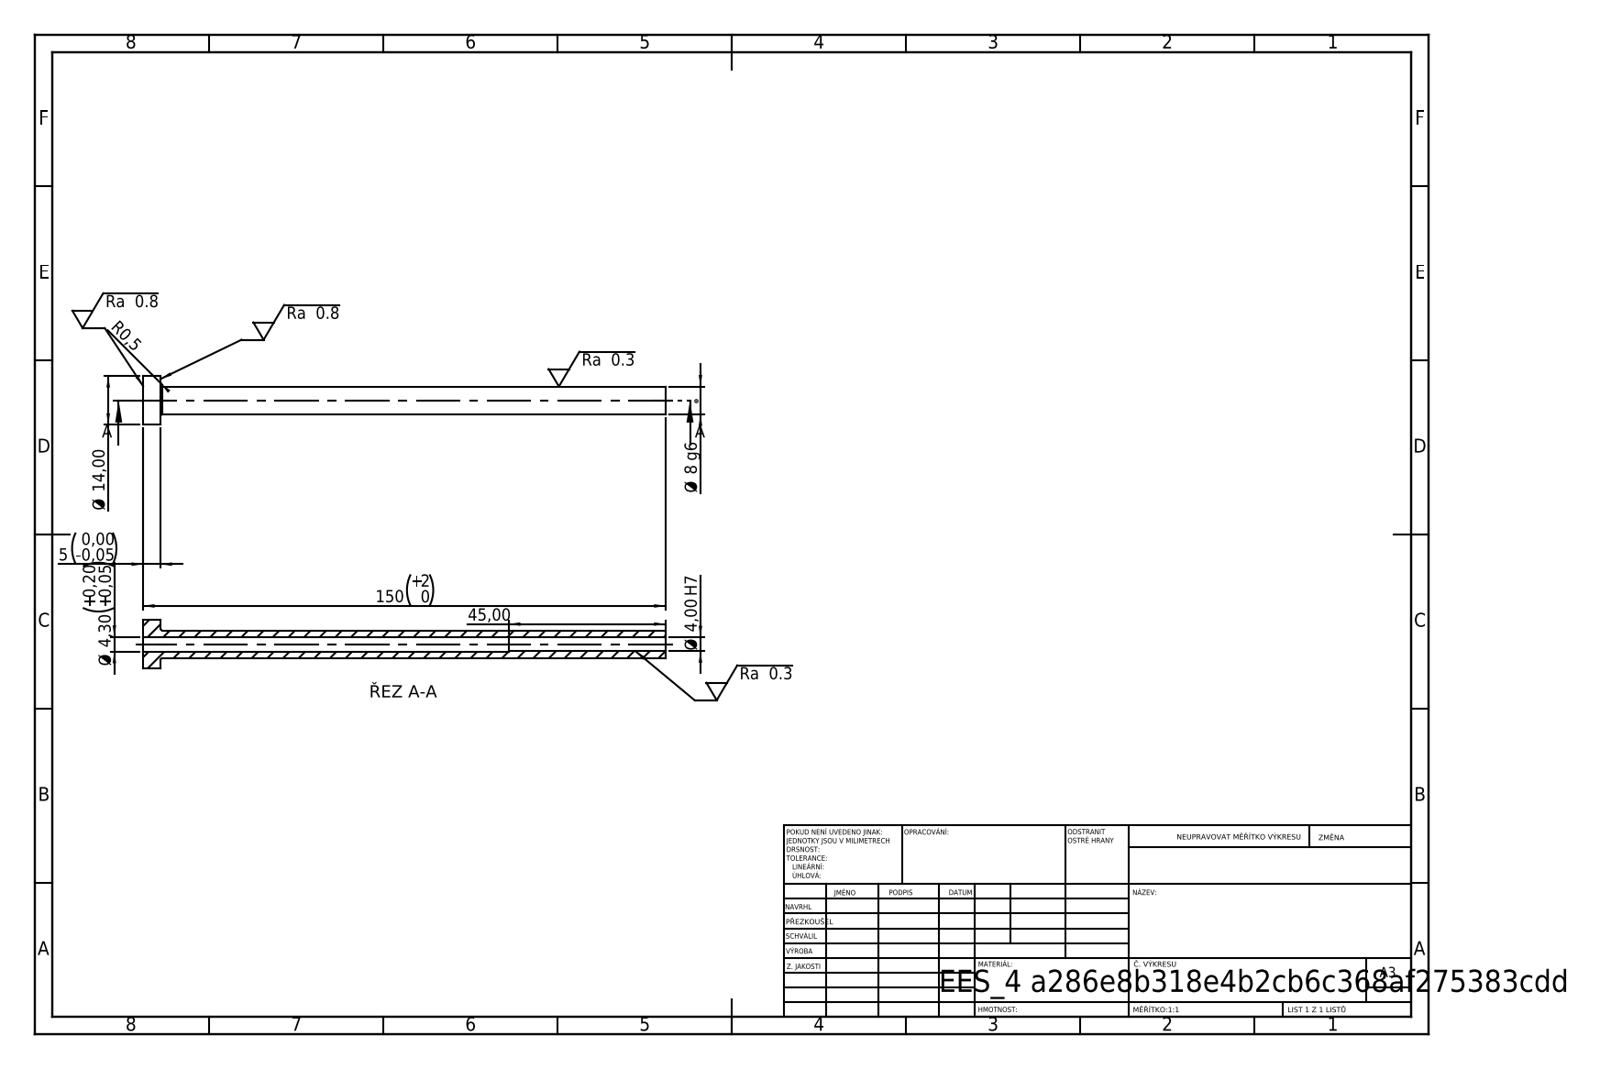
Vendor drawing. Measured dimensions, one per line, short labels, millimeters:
written by: SolidWorks 2019 (CONFIG_CONTROL_DESIGN)
unit: mm
bodies: 1 solid, 14 faces (4 planar, 8 cylindrical, 2 other)
size: 150 × 14 × 14
volume: 5 969 mm³; area: 6 126 mm²
holes: 1× ⌀4, 1× ⌀4.3
bosses: 1× ⌀14, 1× ⌀8
face distances: 5, 150, 145, 105, 100, 45
